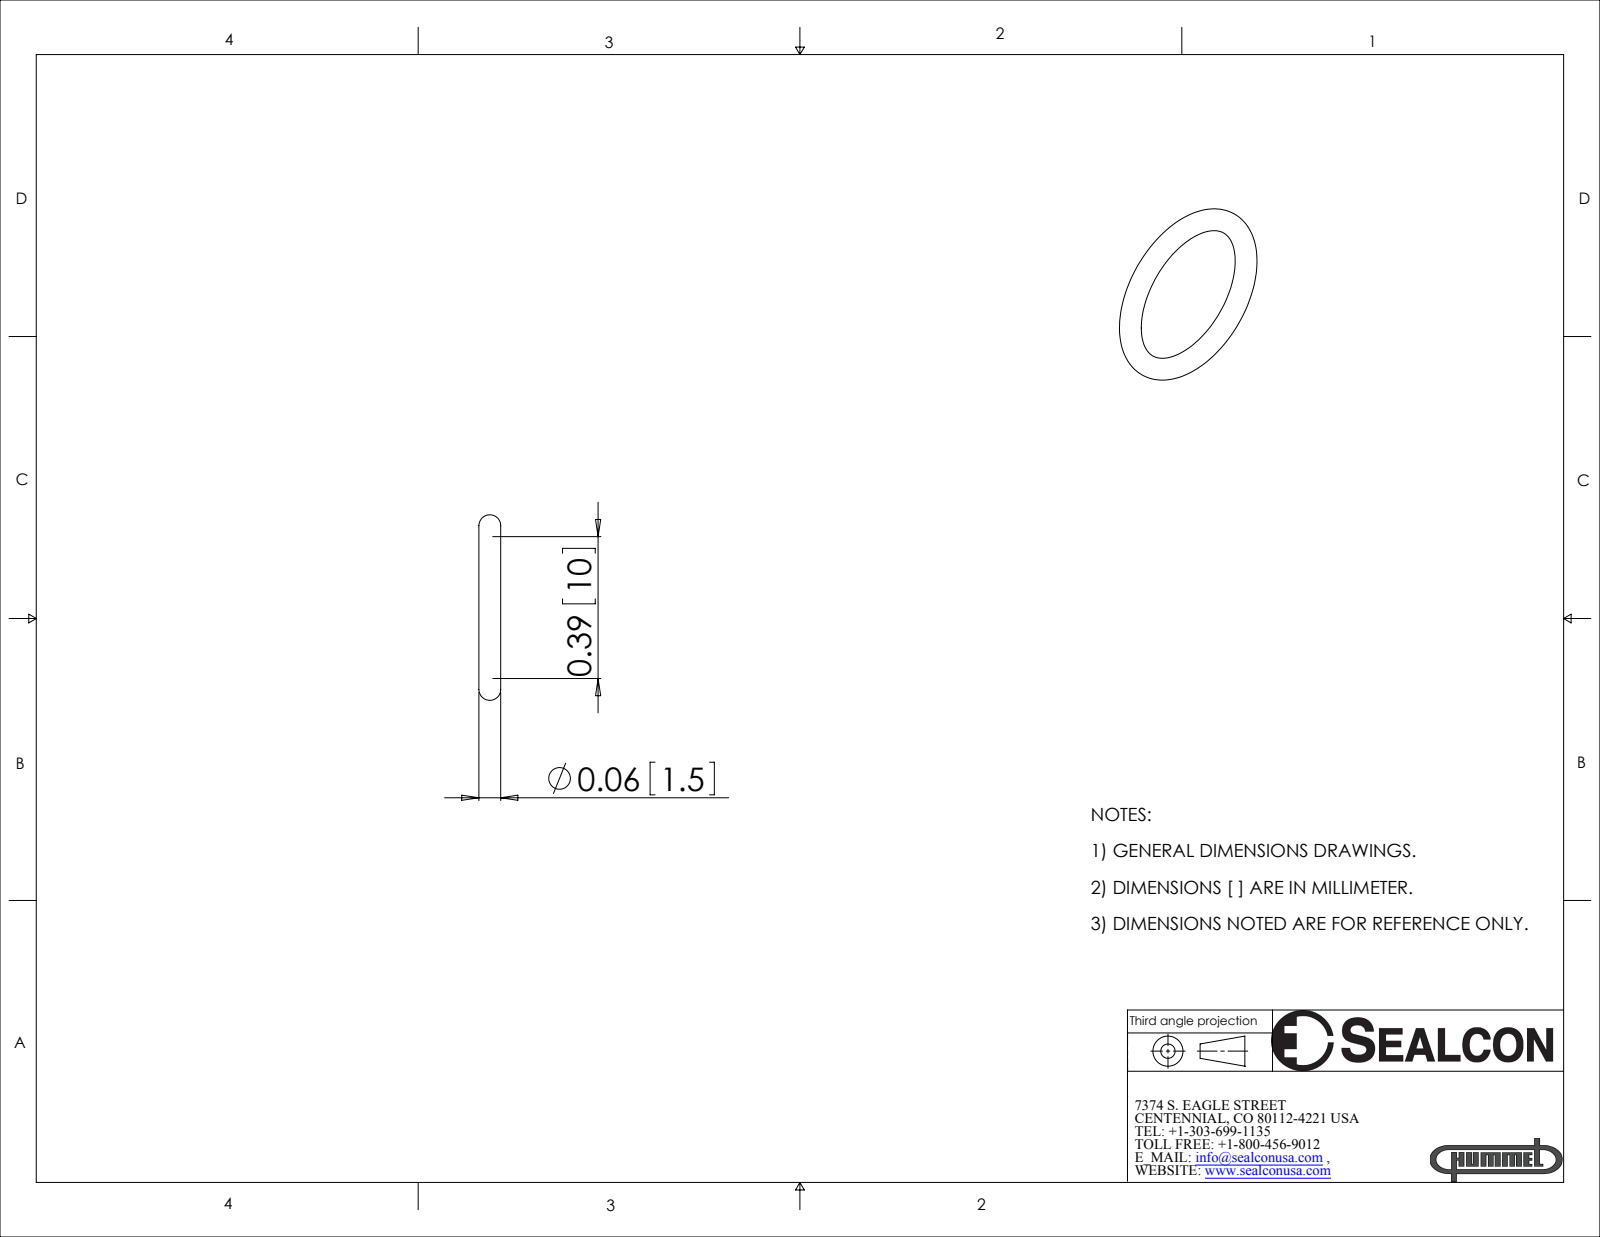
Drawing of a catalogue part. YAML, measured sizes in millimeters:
part_name: "OR-07-SI"
step_written_by: "SolidWorks 2008 (CONFIG_CONTROL_DESIGN)"
units: millimeters
bodies: {solids: 1, faces: 4, planar: 0, cylindrical: 0, other: 4}
overall_size: [13, 13, 1.5]
volume: 70
surface_area: 172
